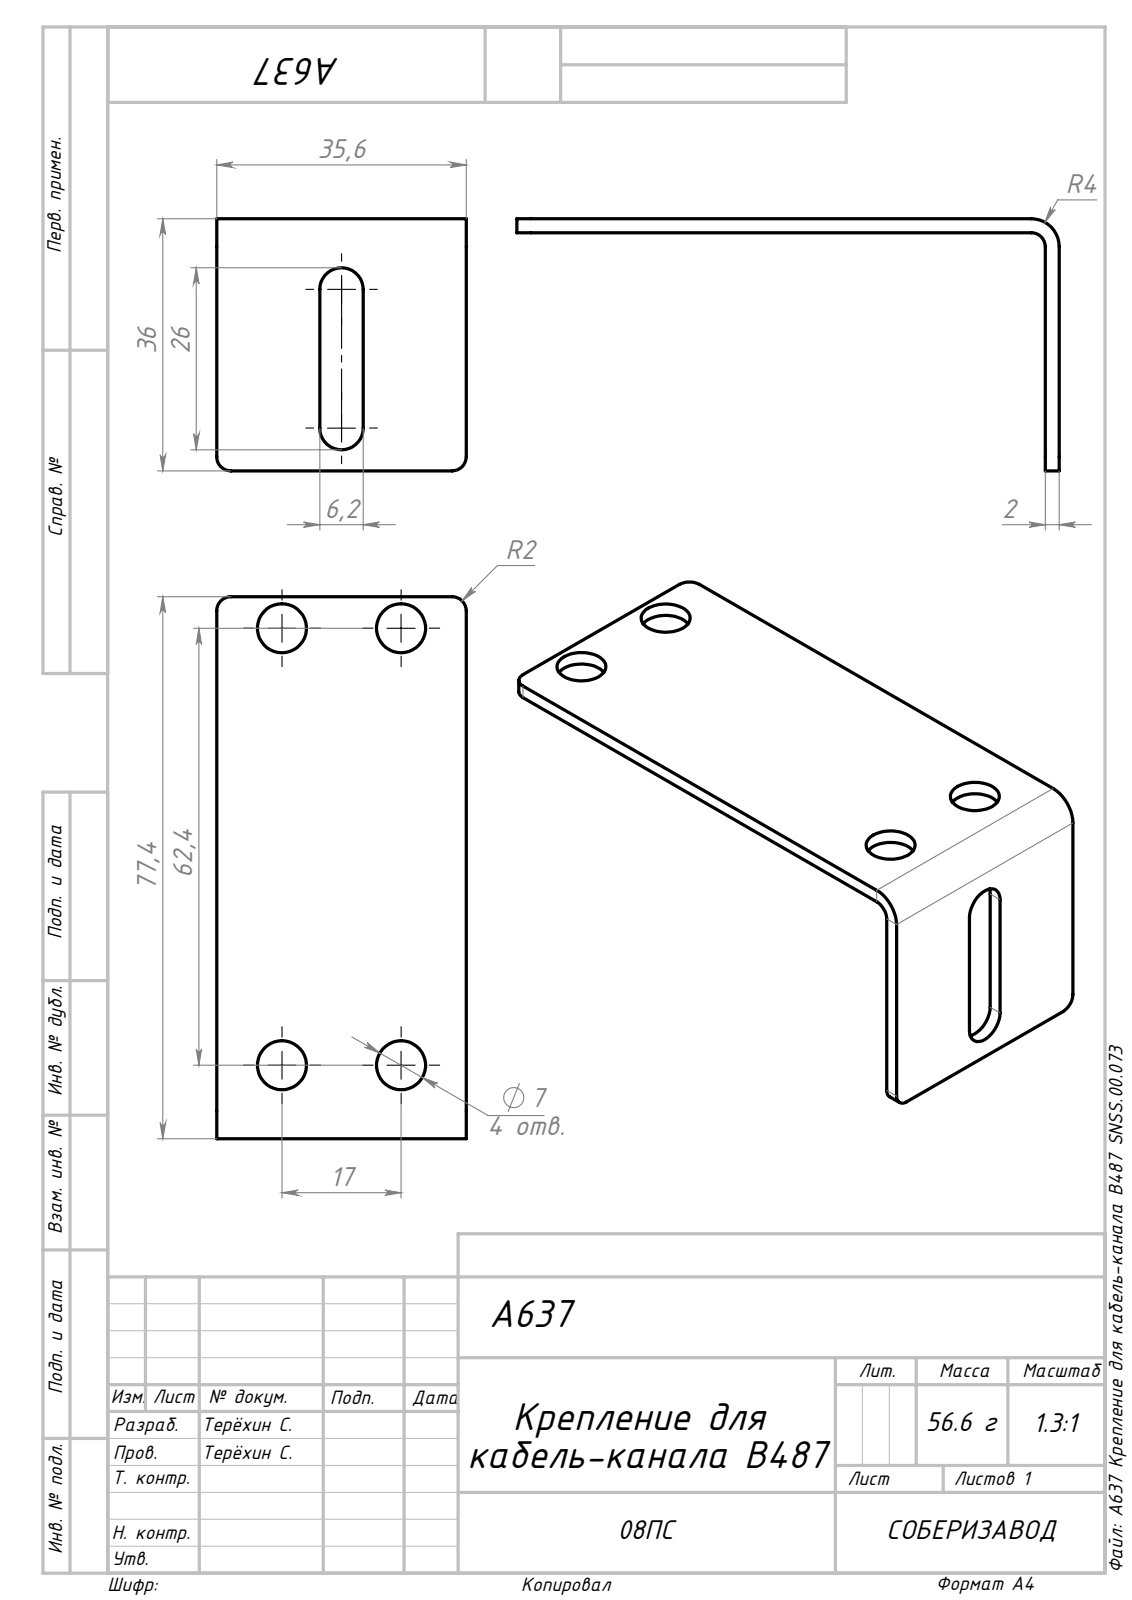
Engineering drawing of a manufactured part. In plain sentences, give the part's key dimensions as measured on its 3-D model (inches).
The part is named "A637 Крепление для кабель-канала B487 SNSS.00.073_1; Сборка1". Its 3-D file was written by "SolidWorks 2022 (AUTOMOTIVE_DESIGN)". It is 1 solid with 31 faces: 14 planar, 17 cylindrical and 0 other. Overall it measures 3.047 by 1.417 by 1.402 inches. Its volume is 0.441 cubic inches and its surface area 12.54 square inches. Round holes: 4 of diameter 0.276. Partial cylindrical surfaces (rounded edges, fillets, slot ends): 5 of radius 0.079, 2 of radius 0.122, 1 of radius 0.157. The main face-to-face distances are 0.079, 1.402, 0.579, 0.823, 1.339, 1.417, 2.969, 3.047, 0.244. The hole center spacings are 0.669, 2.457, 2.546.
